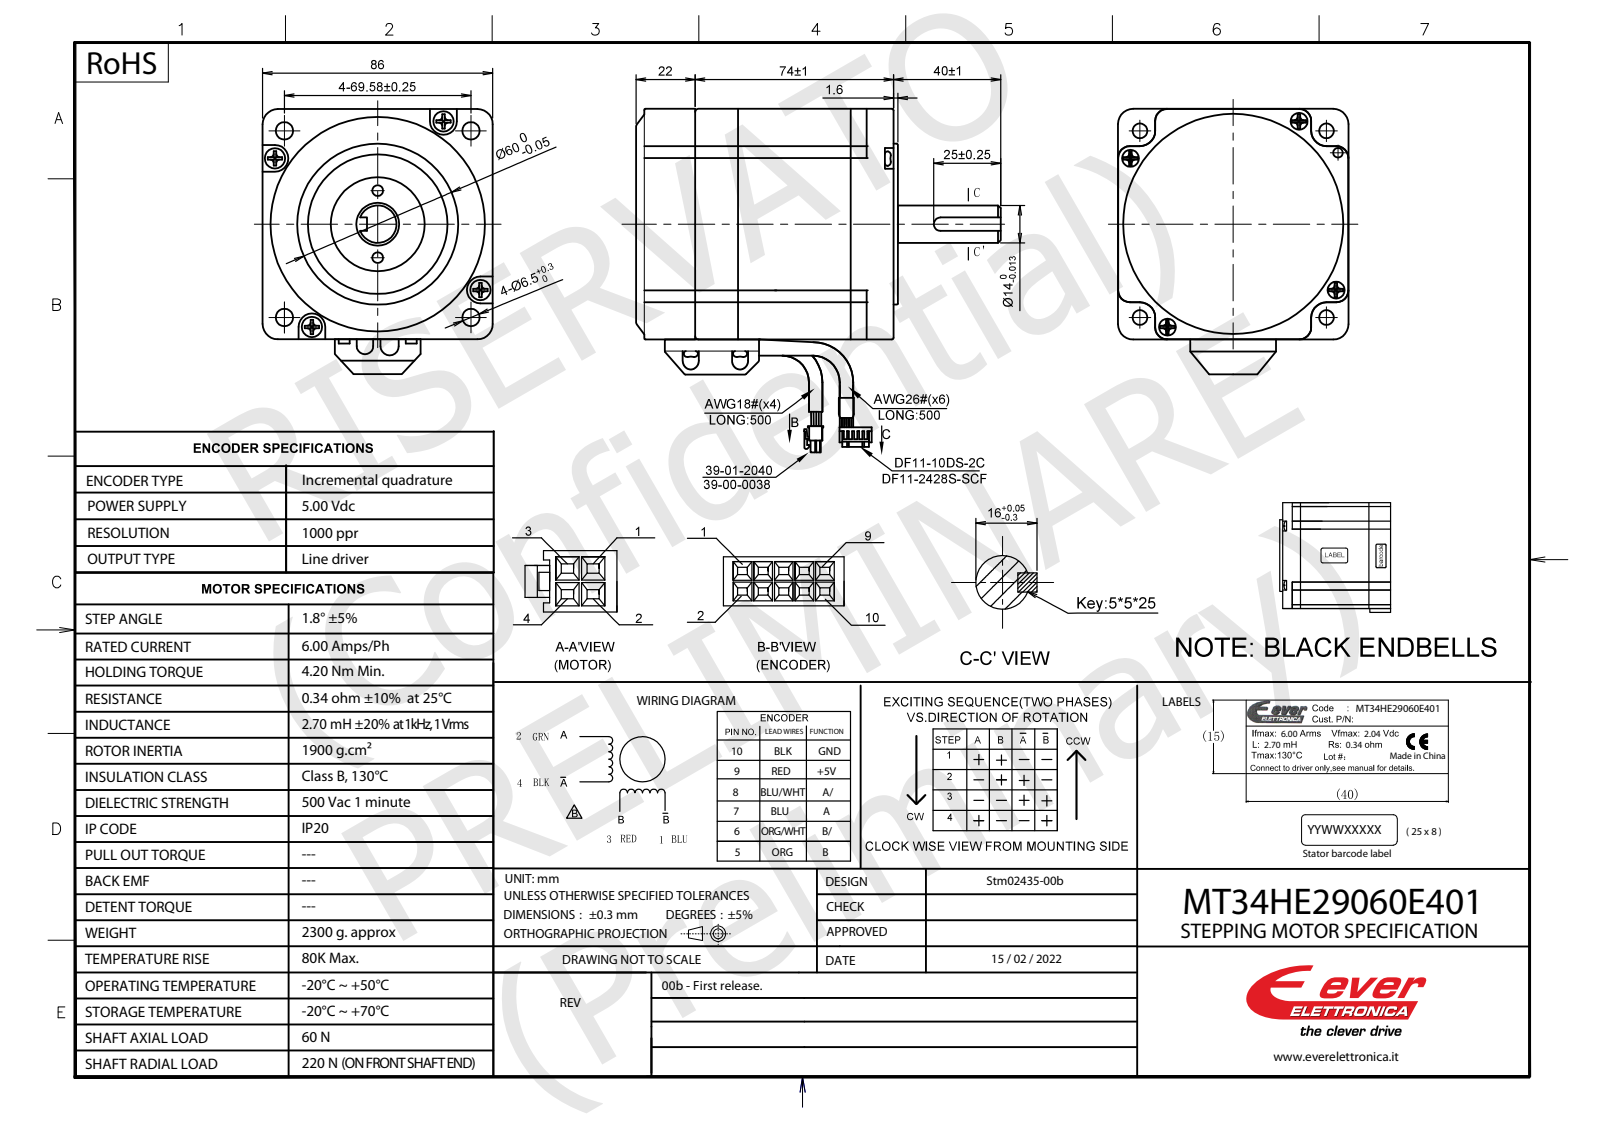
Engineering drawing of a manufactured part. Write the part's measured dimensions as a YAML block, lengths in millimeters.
part_name: "DW34-260-E1000; 11-880; M3x8"
step_written_by: "SolidWorks 2018 (AUTOMOTIVE_DESIGN)"
units: millimeters
bodies: {solids: 97, faces: 45427, planar: 13445, cylindrical: 29564, other: 2418}
overall_size: [136, 105.73, 97.83]
volume: 297018
surface_area: 573993
round_holes:
  - {diameter: 1.6, count: 24}
  - {diameter: 3.2, count: 9}
  - {diameter: 4.5, count: 9}
  - {diameter: 3.3, count: 4}
  - {diameter: 6.3, count: 4}
  - {diameter: 6.5, count: 4}
  - {diameter: 2.5, count: 3}
  - {diameter: 2.75, count: 3}
  - {diameter: 2.74, count: 2}
  - {diameter: 2.76, count: 2}
  - {diameter: 4, count: 2}
  - {diameter: 16, count: 2}
round_bosses_or_shafts:
  - {diameter: 6.4, count: 4}
  - {diameter: 5, count: 4}
  - {diameter: 3, count: 4}
  - {diameter: 2.6, count: 4}
  - {diameter: 56.6, count: 2}
  - {diameter: 55.96, count: 2}
  - {diameter: 10, count: 2}
  - {diameter: 60, count: 1}
partial_cylinders:
  - {radius: 0.2, count: 1316}
  - {radius: 0.6, count: 80}
  - {radius: 1, count: 72}
  - {radius: 1.2, count: 28}
  - {radius: 4.45, count: 26}
  - {radius: 0.5, count: 24}
  - {radius: 3, count: 20}
  - {radius: 5.7, count: 12}
face_to_face_distances: [0.5, 1, 1.5, 2, 2.5, 3, 3.5, 4, 4.5, 5]
hole_center_spacings: [85.77, 44.4, 82.04, 83.76, 89.55, 10.34, 20.5, 33.98]
